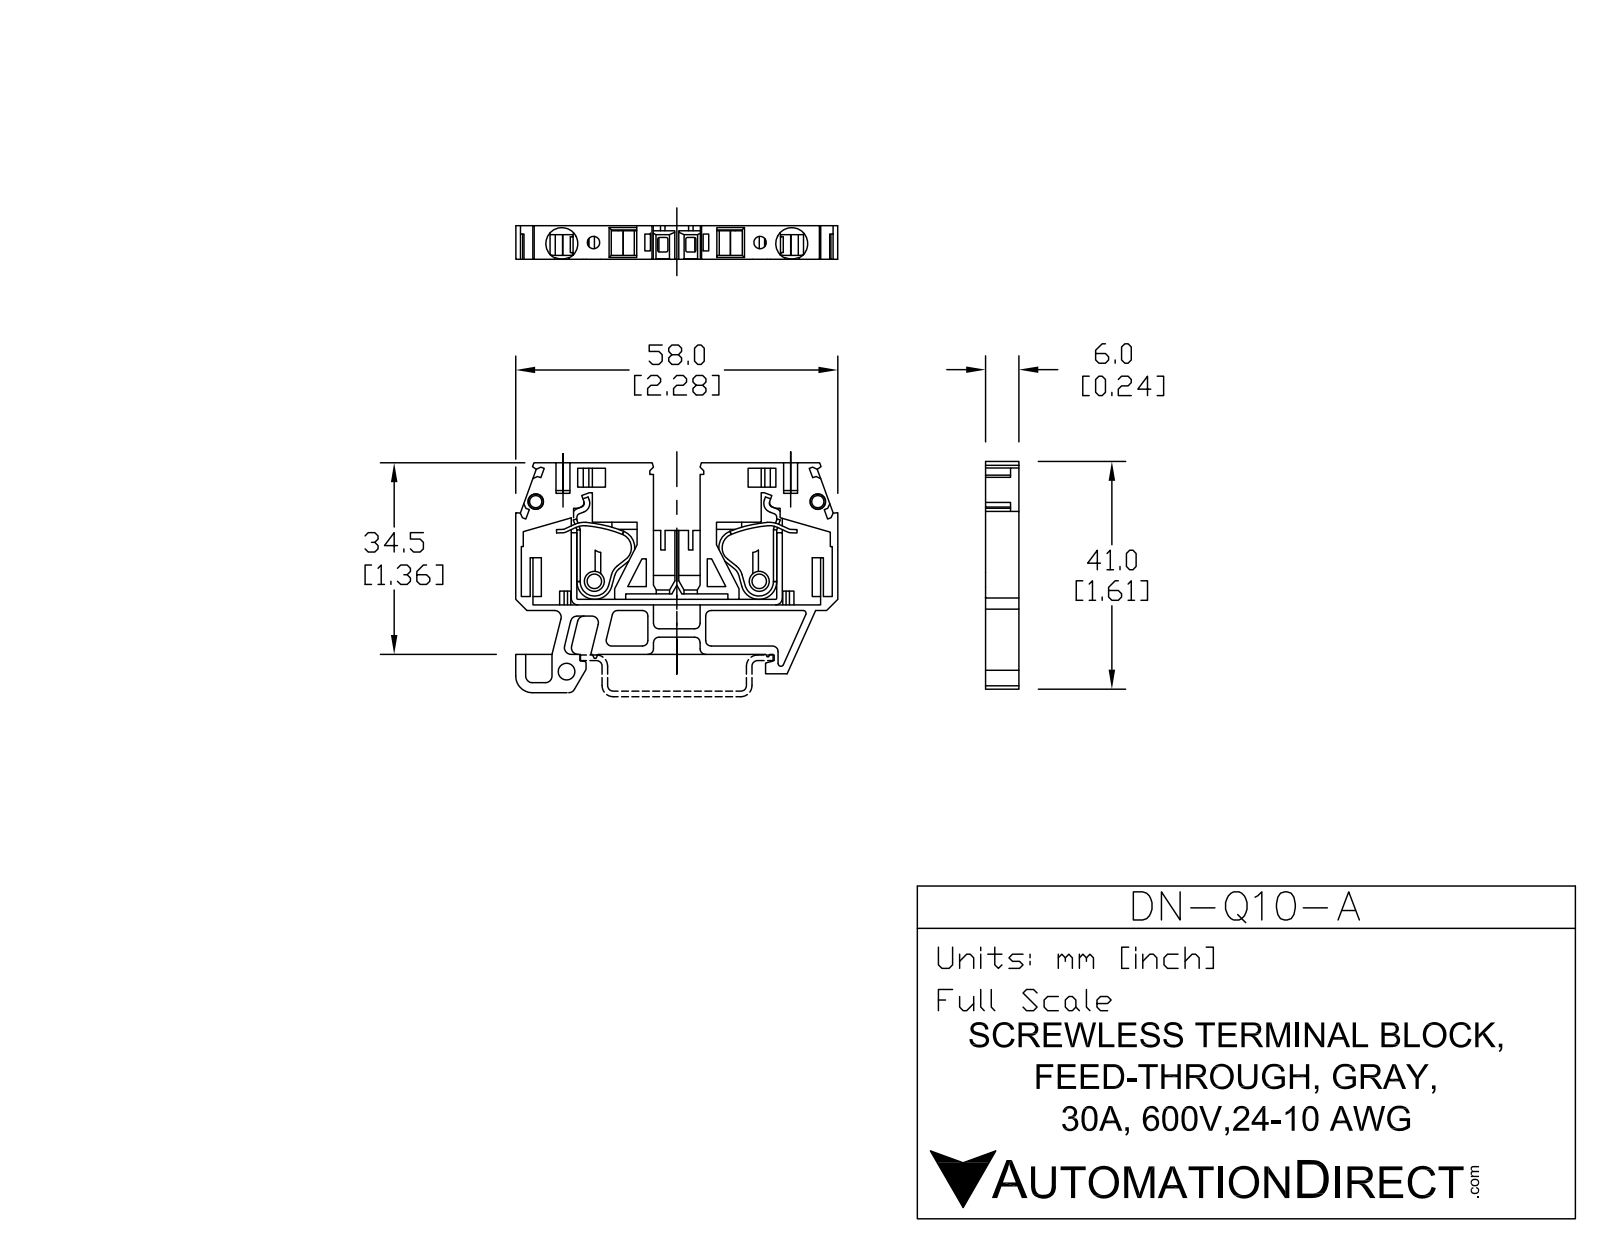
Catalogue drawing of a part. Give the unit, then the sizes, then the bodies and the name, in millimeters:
Units: millimetres
Overall size (bounding box): 57.4 × 41 × 6
Round holes (diameter × count): ⌀2.2 ×2, ⌀2.8 ×2, ⌀5.7 ×2, ⌀3 ×1
Round bosses / shafts (diameter × count): ⌀3.6 ×2
Partial cylindrical surfaces — rounded edges, fillets, slot ends (radius × count): R1 ×13, R1.2 ×11, R0.3 ×9, R0.2 ×6, R0.7 ×4, R0.8 ×4, R1.7 ×4, R2.6 ×4
Main face-to-face distances: 0.9, 6, 1, 5.1, 2, 5.9, 0.8, 4, 3.9, 1.9
Hole centre spacings: 5.6, 35.4, 29.7, 30.7, 41, 50.2, 54.2
Volume: 5 520 mm³ · Surface area: 9 929 mm²
Bodies: 10 solids, 564 faces (411 planar, 129 cylindrical, 24 other)
Part name (STEP PRODUCT): DN-Q10-A
STEP written by: SolidWorks 2019 (AUTOMOTIVE_DESIGN)
